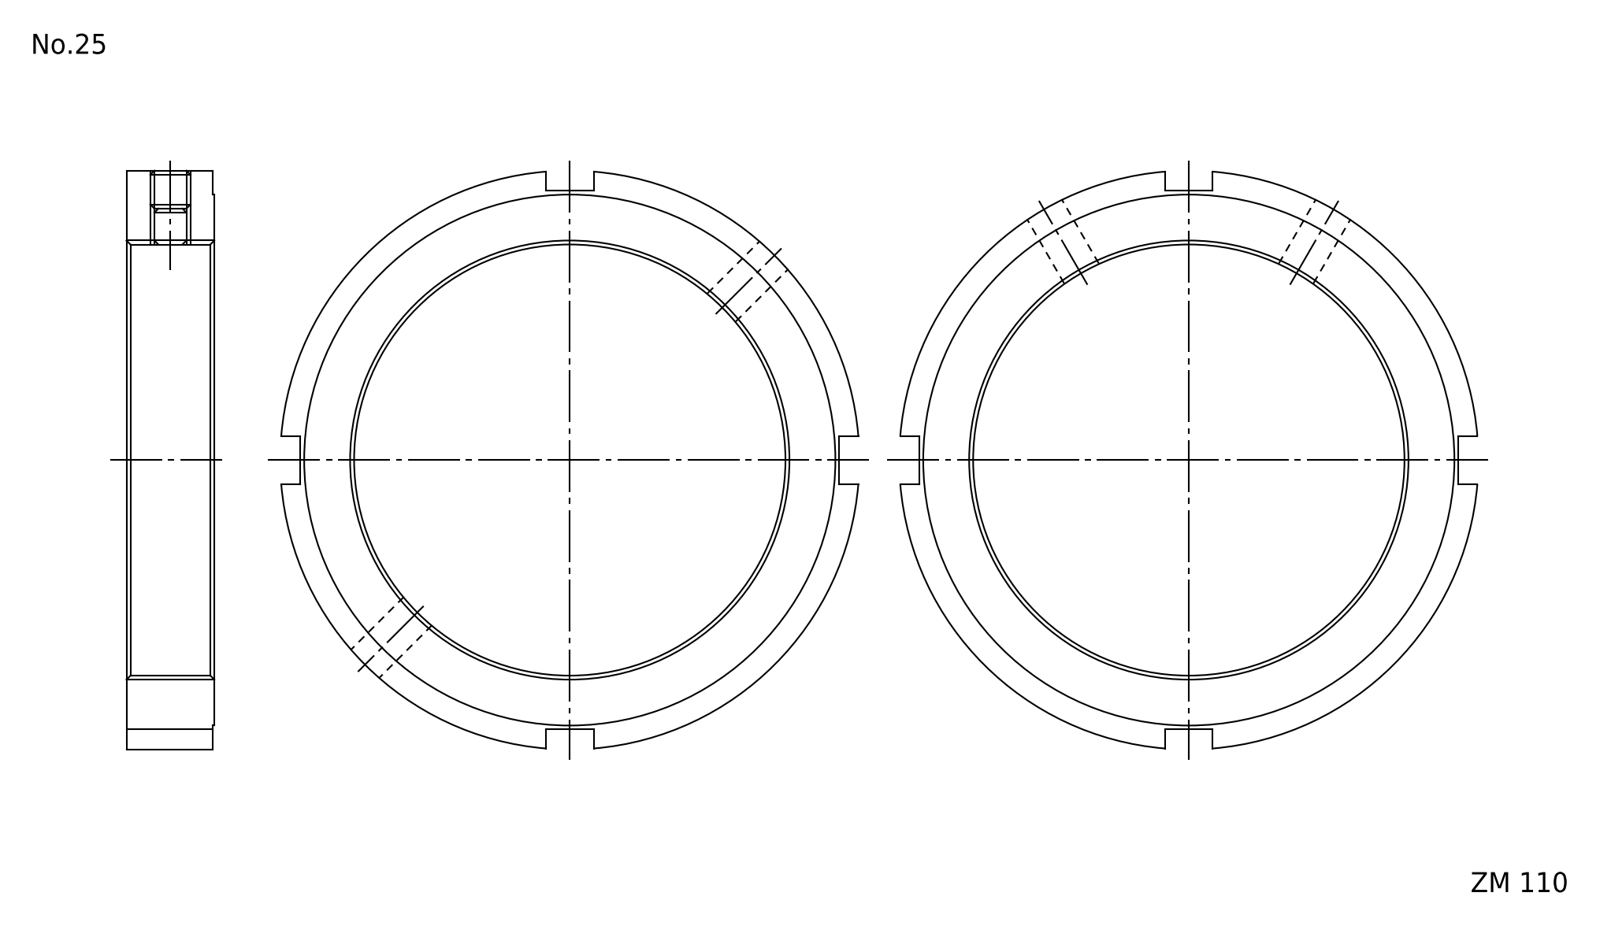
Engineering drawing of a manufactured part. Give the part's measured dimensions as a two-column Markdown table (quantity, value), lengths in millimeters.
| quantity | value |
| --- | --- |
| part name | FKD ZM110 |
| STEP written by | Autodesk Inventor 2011 (AUTOMOTIVE_DESIGN) |
| units | millimeters |
| bodies | 1 solid, 23 faces (15 planar, 8 cylindrical, 0 other) |
| overall size | 144.5 × 144.5 × 22 |
| volume | 145 899 mm³ |
| surface area | 32 670 mm² |
| round holes (diameter × count) | 8.38 × 2, 110 × 1 |
| round bosses / shafts (diameter × count) | 145 × 1, 133 × 1 |
| main face-to-face distances | 22, 0.5, 21.5, 61.5, 73.5, 135, 12 |
